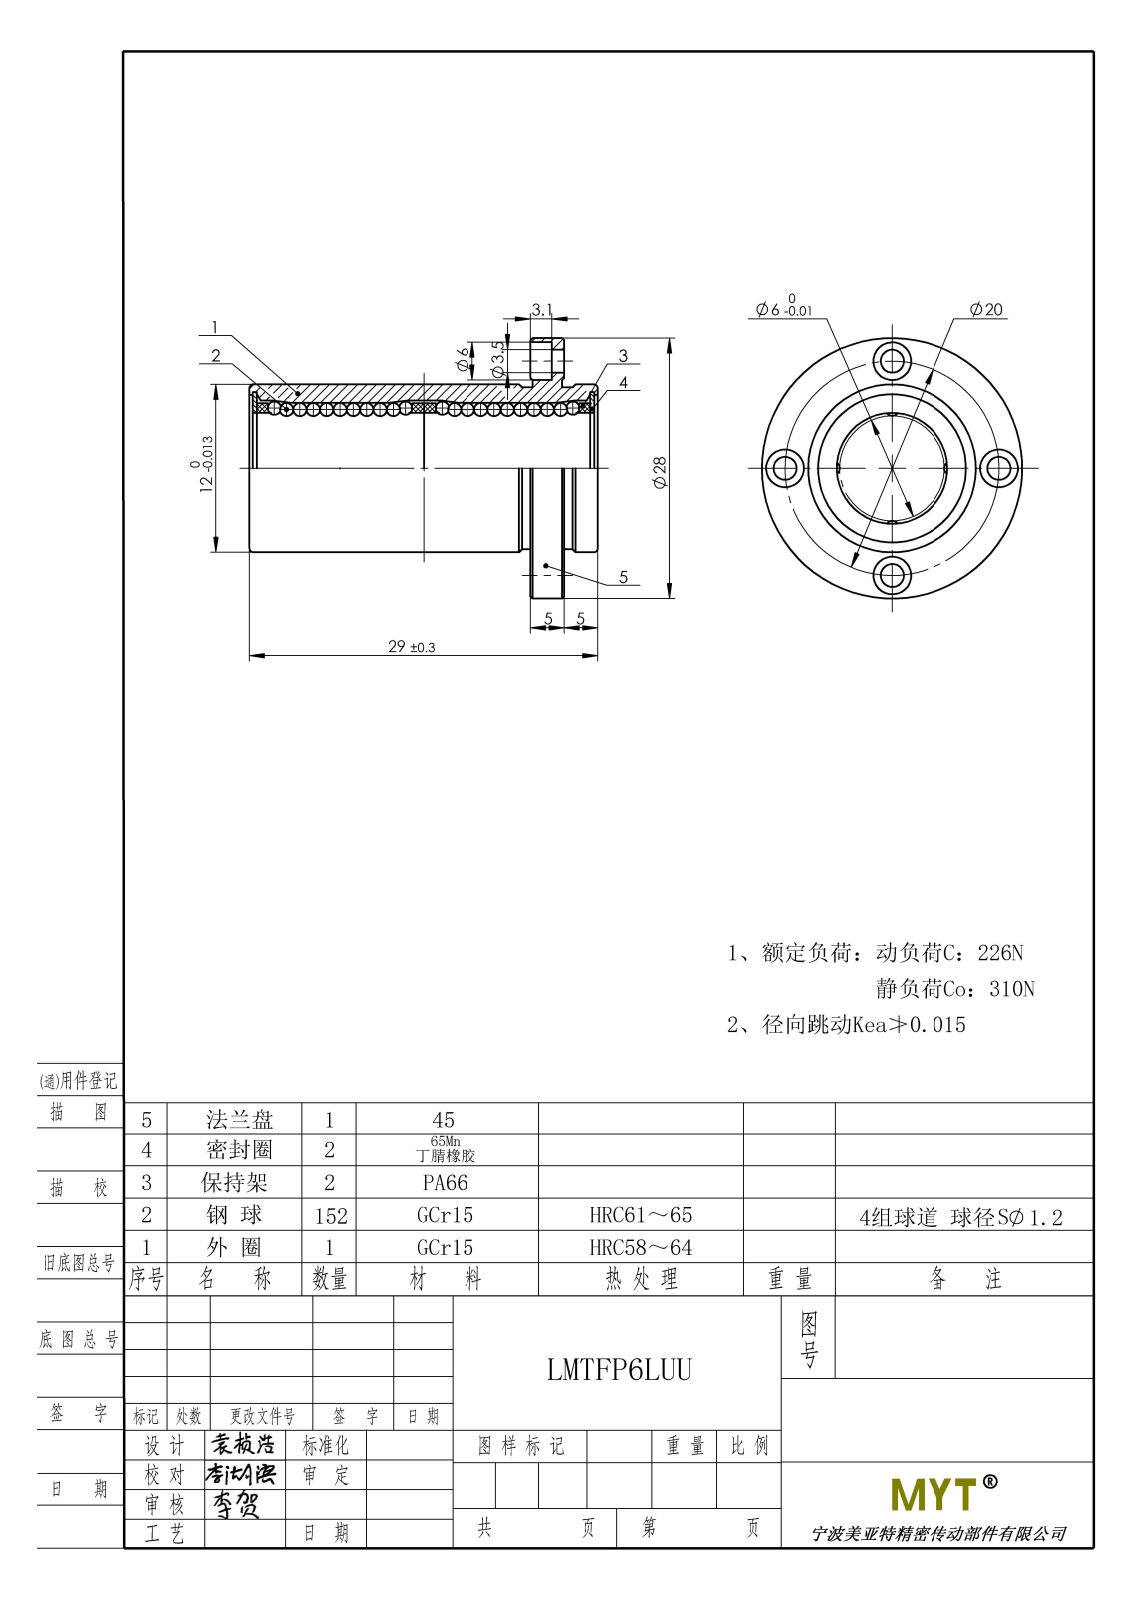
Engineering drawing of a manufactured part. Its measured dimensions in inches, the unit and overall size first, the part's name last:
Units: inches
Overall size (bounding box): 1.142 × 1.102 × 1.102
Round holes (diameter × count): ⌀0.236 ×5, ⌀0.138 ×4, ⌀0.252 ×1, ⌀0.268 ×1
Round bosses / shafts (diameter × count): ⌀1.102 ×1, ⌀0.472 ×1
Main face-to-face distances: 0.197, 0.075, 0.122, 0.945, 0.87, 0.748, 0.272, 0.394, 1.142, 0.031
Hole centre spacings: 0.394, 0.557, 0.787
Volume: 0.276 in³ · Surface area: 5.048 in²
Bodies: 1 solid, 32 faces (12 planar, 16 cylindrical, 4 other)
Part name (STEP PRODUCT): LMTFP6LUU
STEP written by: PARTsolutions (CONFIG_CONTROL_DESIGN)
